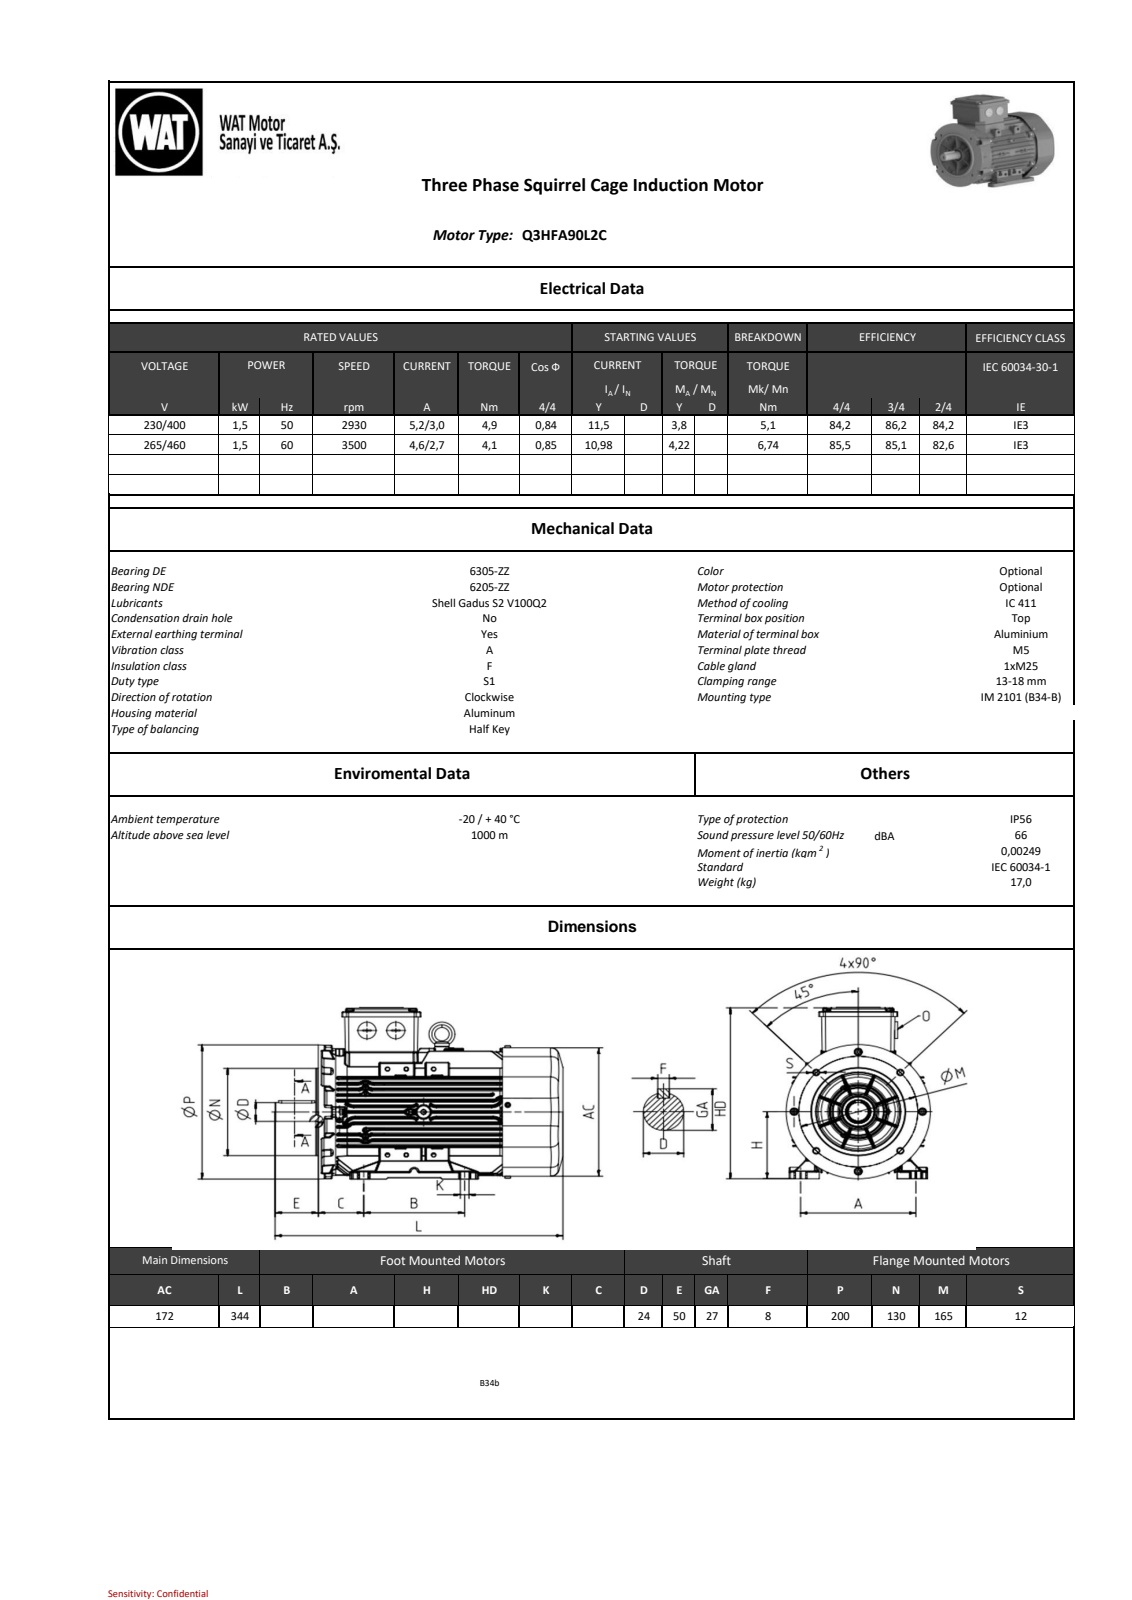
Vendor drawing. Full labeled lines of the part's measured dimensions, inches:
Part name (STEP PRODUCT): model1
STEP written by: SIEMENS PLM Software NX2206.8101 (AUTOMOTIVE_DESIGN)
Units: inches
Bodies: 0 solids, 5029 faces (1251 planar, 2208 cylindrical, 1570 other)
Overall size (bounding box): 13.525 × 9.175 × 7.874
Round holes (diameter × count): ⌀0.433 ×4, ⌀0.472 ×4, ⌀0.389 ×1, ⌀1.473 ×1, ⌀3.141 ×1, ⌀3.85 ×1, ⌀4.558 ×1
Round bosses / shafts (diameter × count): ⌀0.315 ×7, ⌀0.197 ×6, ⌀0.984 ×3, ⌀7.874 ×1, ⌀5.118 ×1, ⌀4.023 ×1, ⌀3.315 ×1, ⌀1.083 ×1
Partial cylindrical surfaces — rounded edges, fillets, slot ends (radius × count): R0.039 ×682, R0.031 ×533, R0.02 ×78, R0.079 ×77, R0.315 ×28, R0.157 ×10, R0.224 ×6, R0.028 ×4
Main face-to-face distances: 0.295, 3.619, 0.352, 3.267, 0.928, 1.982, 0.29, 3.557, 0.049, 0.664
Hole centre spacings: 2.441, 5.887, 3.126, 3.246, 4.42, 4.591, 3.245, 3.248
